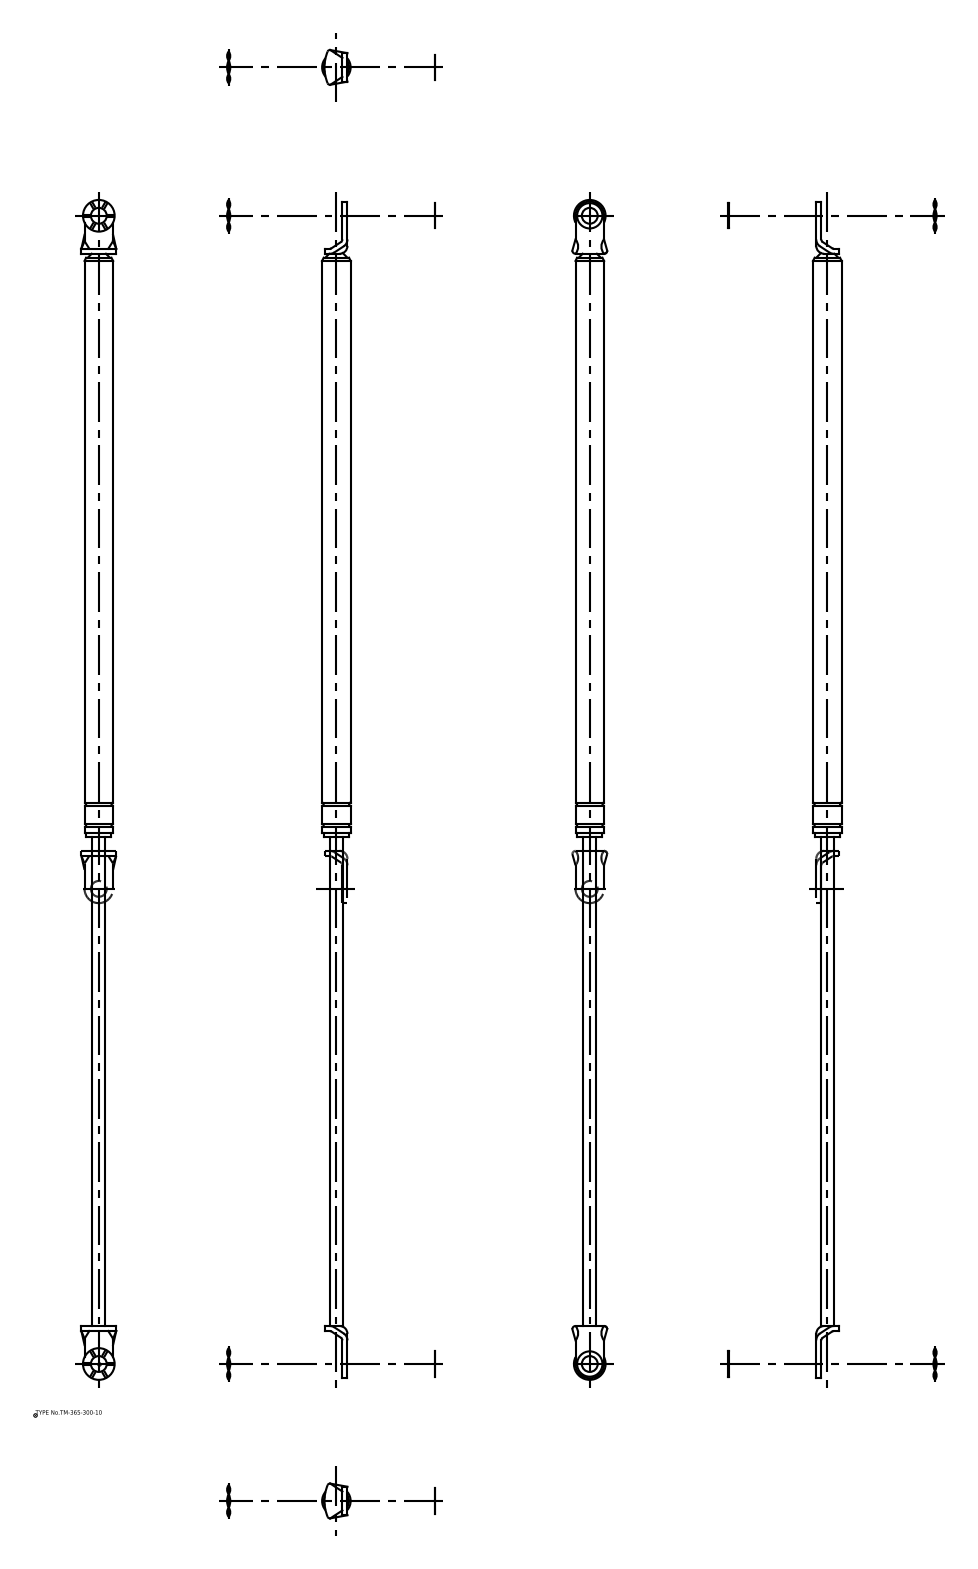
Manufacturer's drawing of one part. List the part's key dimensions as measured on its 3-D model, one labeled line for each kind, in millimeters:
Part name (STEP PRODUCT): ウェーブワッシャー; ワッシャー; 本体; 本体_div
STEP written by: spGate 16.7.1 (AUTOMOTIVE_DESIGN)
Units: millimetres
Bodies: 6 solids, 94 faces (42 planar, 44 cylindrical, 8 other)
Overall size (bounding box): 745 × 22 × 18.5
Volume: 114 163 mm³ · Surface area: 34 589 mm²
Round holes (diameter × count): ⌀10 ×2
Round bosses / shafts (diameter × count): ⌀16 ×3, ⌀20 ×2, ⌀18.5 ×1, ⌀18 ×1, ⌀8 ×1
Partial cylindrical surfaces — rounded edges, fillets, slot ends (radius × count): R4.4 ×2, R5 ×2, R9 ×2, R26.32 ×1
Main face-to-face distances: 3.2, 2, 5.2, 680.2, 3.7, 5.7, 0.5, 371.2, 312.2, 683.4
Hole centre spacings: 725
